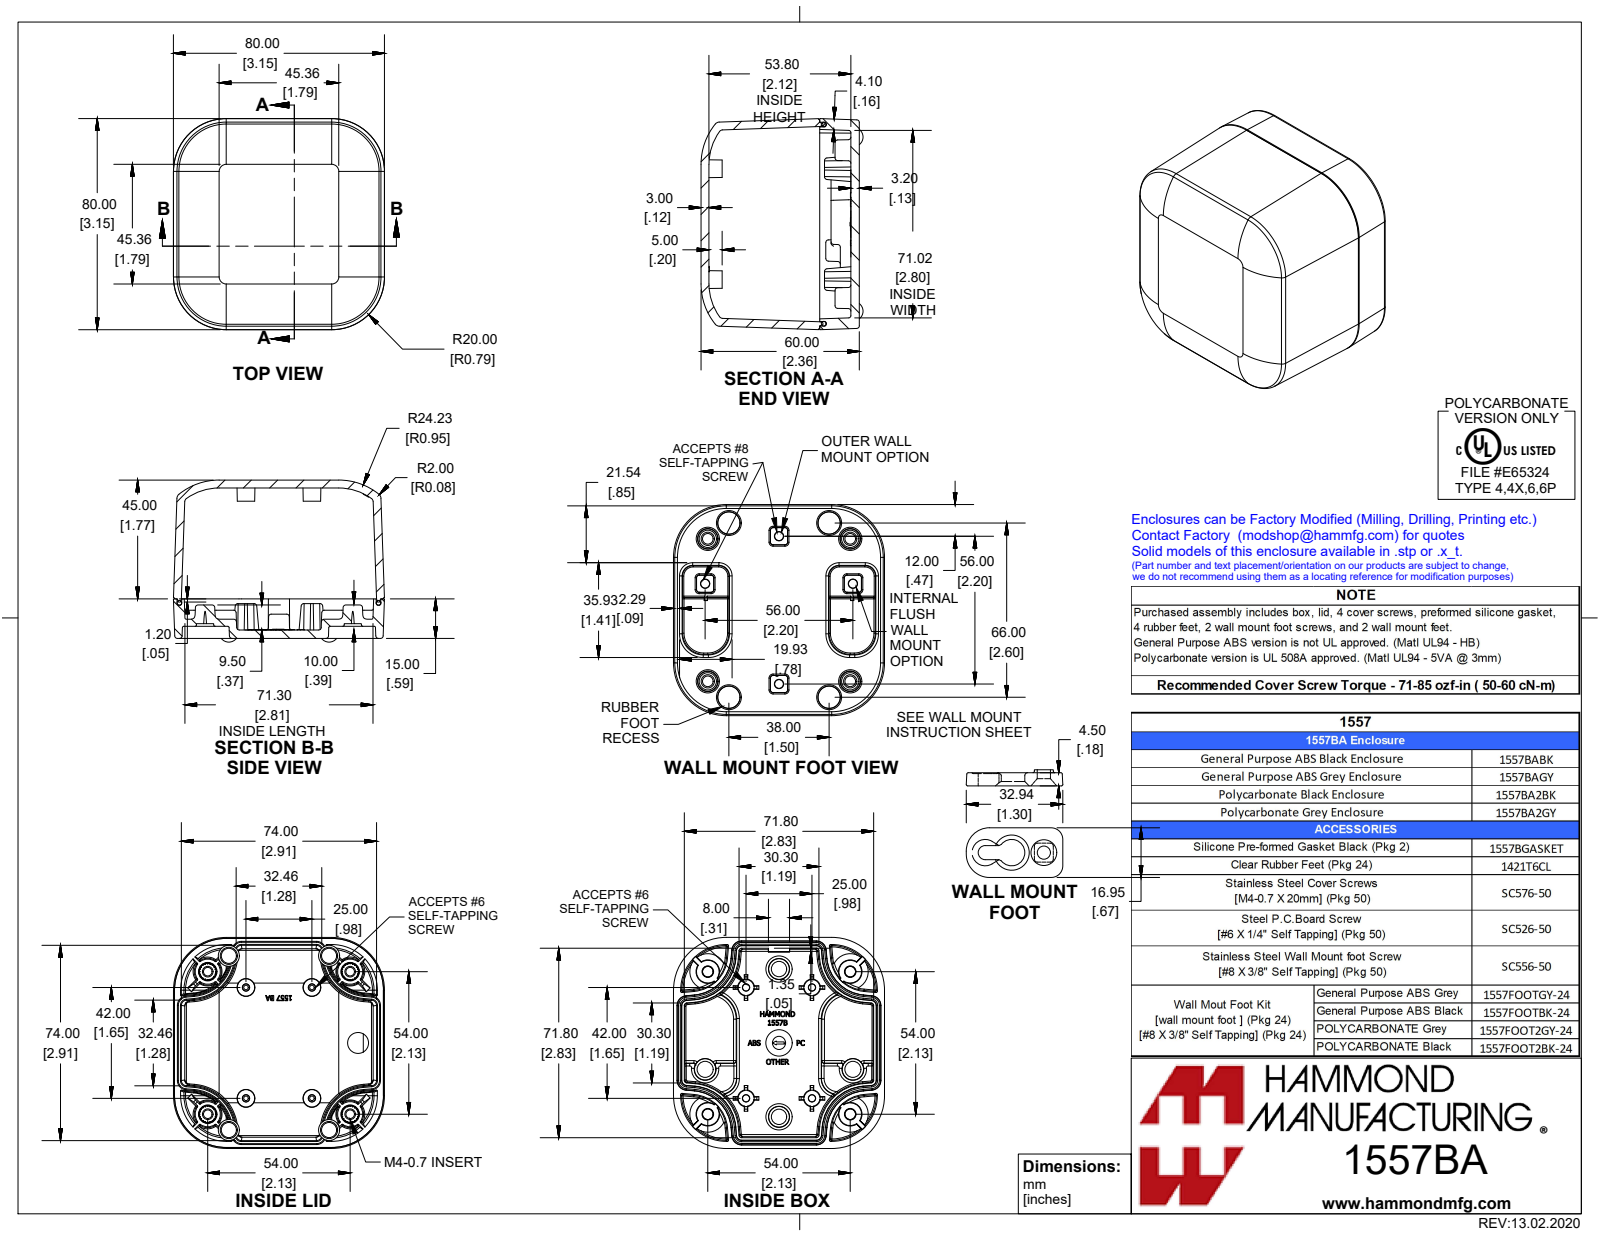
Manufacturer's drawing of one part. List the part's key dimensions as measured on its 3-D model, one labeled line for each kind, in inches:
Part name (STEP PRODUCT): IN-M4 (insert M4-0.7X5.75mm SS) KNURLS; PFR1421T4; 1557B Bottom; Wall Mount Foot (+5 more)
STEP written by: SolidWorks 2019 (CONFIG_CONTROL_DESIGN)
Units: inches
Bodies: 19 solids, 2489 faces (823 planar, 471 cylindrical, 1195 other)
Overall size (bounding box): 4.289 × 3.15 × 2.539
Volume: 7.122 in³ · Surface area: 136.2 in²
Round holes (diameter × count): ⌀0.128 ×4, ⌀0.177 ×2
Round bosses / shafts (diameter × count): ⌀0.071 ×12, ⌀0.313 ×4, ⌀0.25 ×4, ⌀0.218 ×4, ⌀0.21 ×4, ⌀0.153 ×4, ⌀0.135 ×4, ⌀0.303 ×2
Partial cylindrical surfaces — rounded edges, fillets, slot ends (radius × count): R0.02 ×104, R0.039 ×53, R0.079 ×12, R0.012 ×8, R0.059 ×8, R0.157 ×8, R0.315 ×6, R0.836 ×4
Main face-to-face distances: 0.118, 3.029, 3.146, 0.118, 2.362, 0.126, 2.236, 2.244, 2.118, 1.654
Hole centre spacings: 1.064, 2.126, 2.412, 3.007, 2.205
